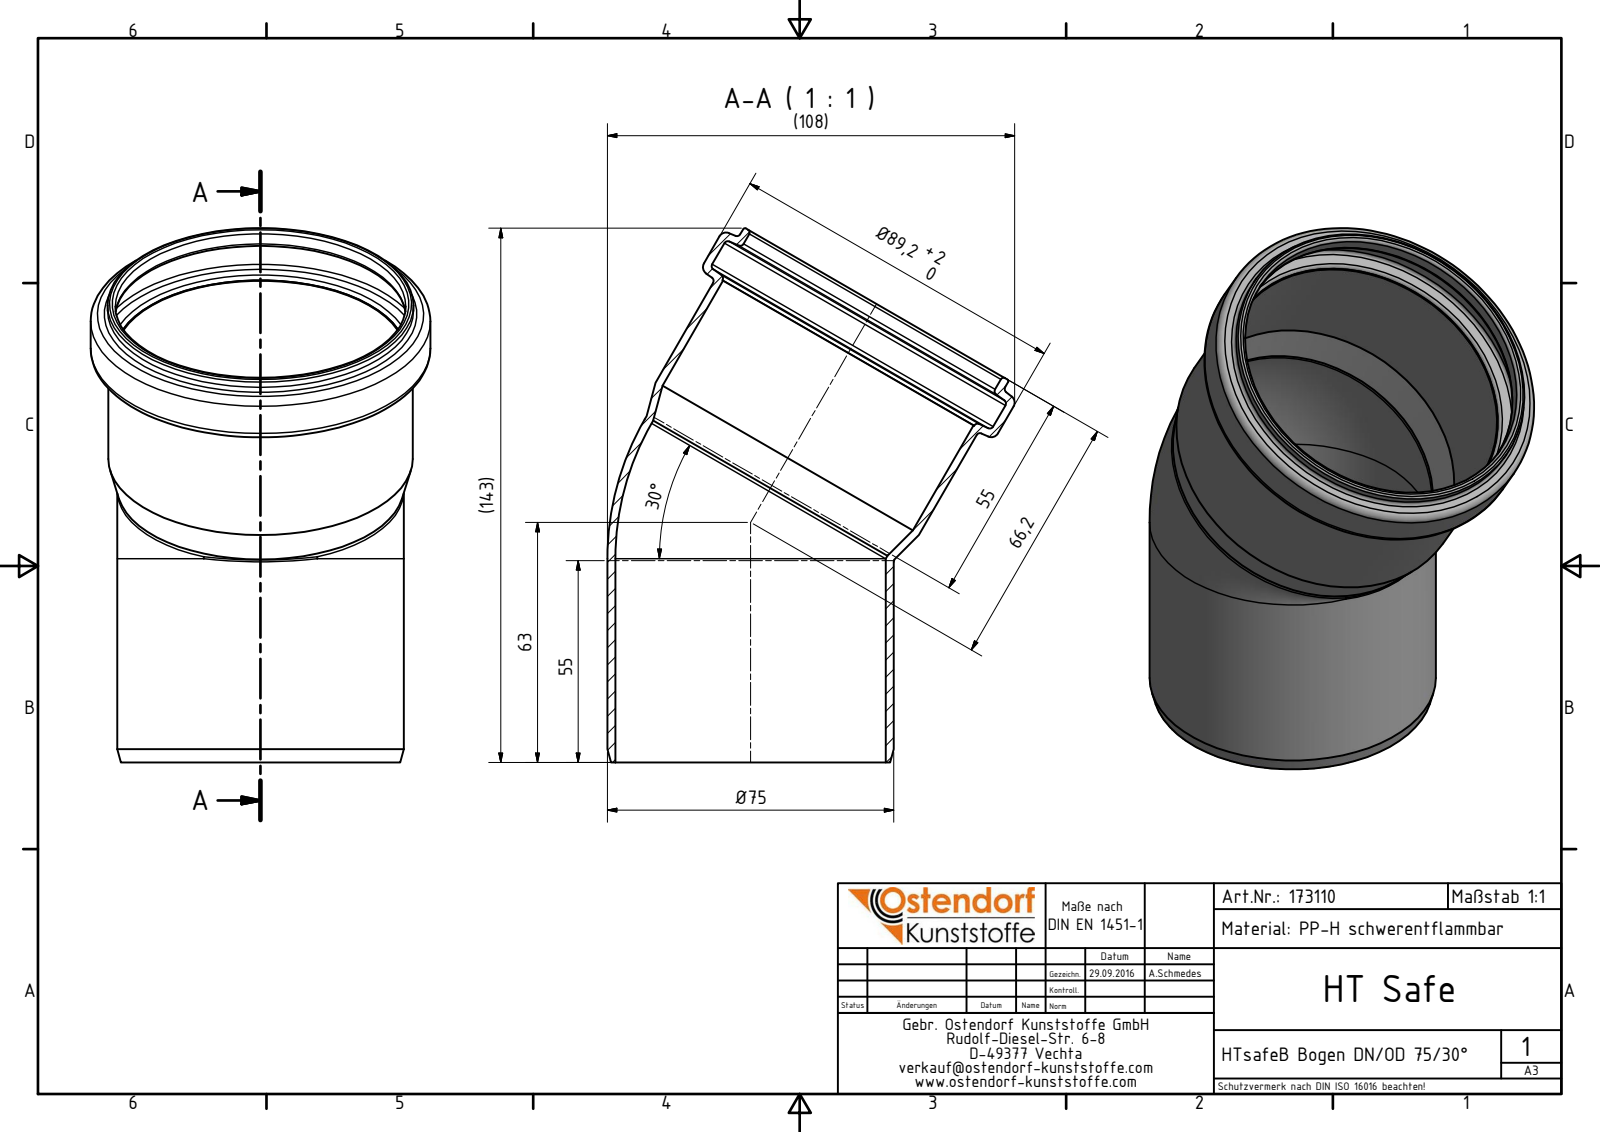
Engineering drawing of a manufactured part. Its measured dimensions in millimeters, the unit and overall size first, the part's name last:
Units: millimetres
Overall size (bounding box): 140.22 × 106.95 × 89.2
Round holes (diameter × count): ⌀71 ×2, ⌀75.9 ×1, ⌀76.3 ×1, ⌀85.2 ×1
Round bosses / shafts (diameter × count): ⌀75.2 ×2, ⌀89.2 ×1, ⌀80.3 ×1, ⌀79.9 ×1
Main face-to-face distances: 14.89
Volume: 65 789 mm³ · Surface area: 65 494 mm²
Bodies: 1 solid, 34 faces (3 planar, 11 cylindrical, 20 other)
Part name (STEP PRODUCT): 173110 HTsafeB DN_OD 75_30°
STEP written by: Autodesk Inventor 2016 (AUTOMOTIVE_DESIGN)
